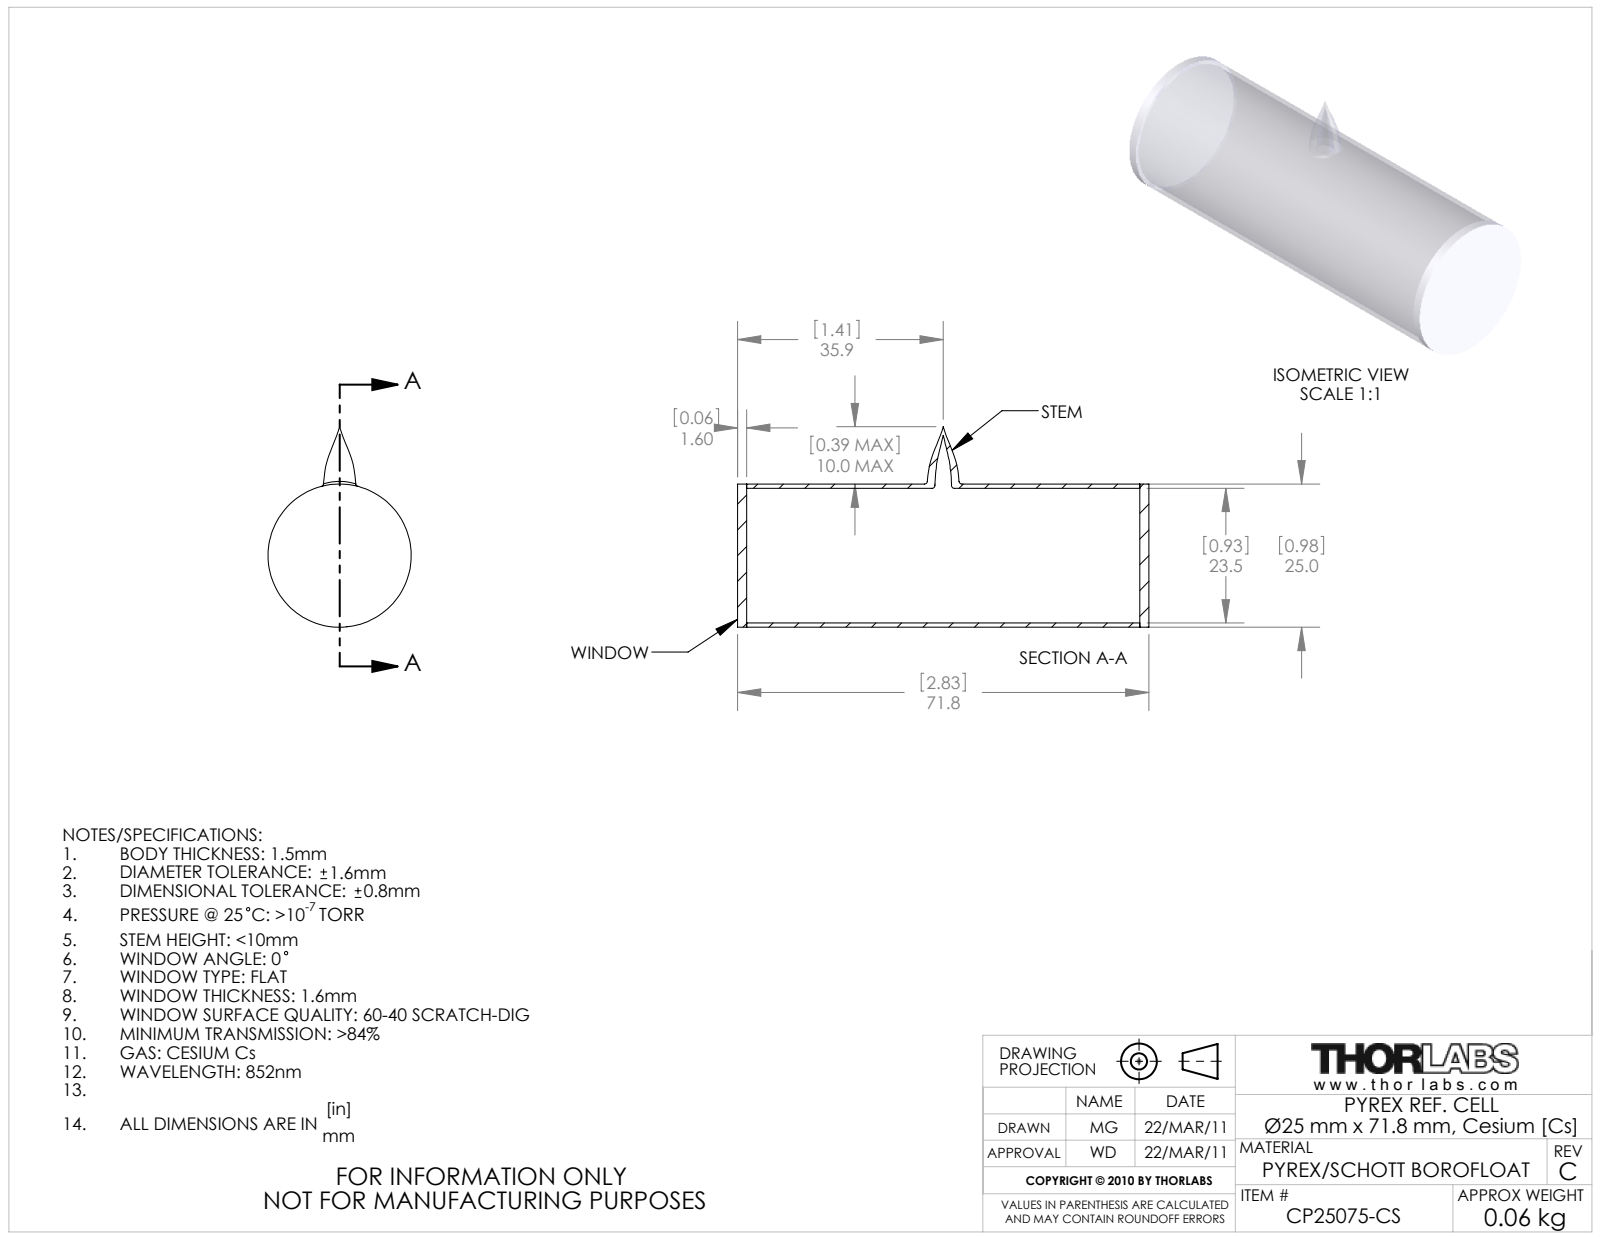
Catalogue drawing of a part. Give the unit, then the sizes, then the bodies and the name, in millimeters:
Units: millimetres
Overall size (bounding box): 71.84 × 35 × 25
Round holes (diameter × count): ⌀2.91 ×1, ⌀23.5 ×1
Round bosses / shafts (diameter × count): ⌀25 ×1
Main face-to-face distances: 1.6, 70.24, 68.64, 71.84
Volume: 5 577 mm³ · Surface area: 12 920 mm²
Bodies: 3 solids, 24 faces (6 planar, 10 cylindrical, 8 other)
Part name (STEP PRODUCT): 12094-E0W
STEP written by: SolidWorks 2009 (AUTOMOTIVE_DESIGN)
